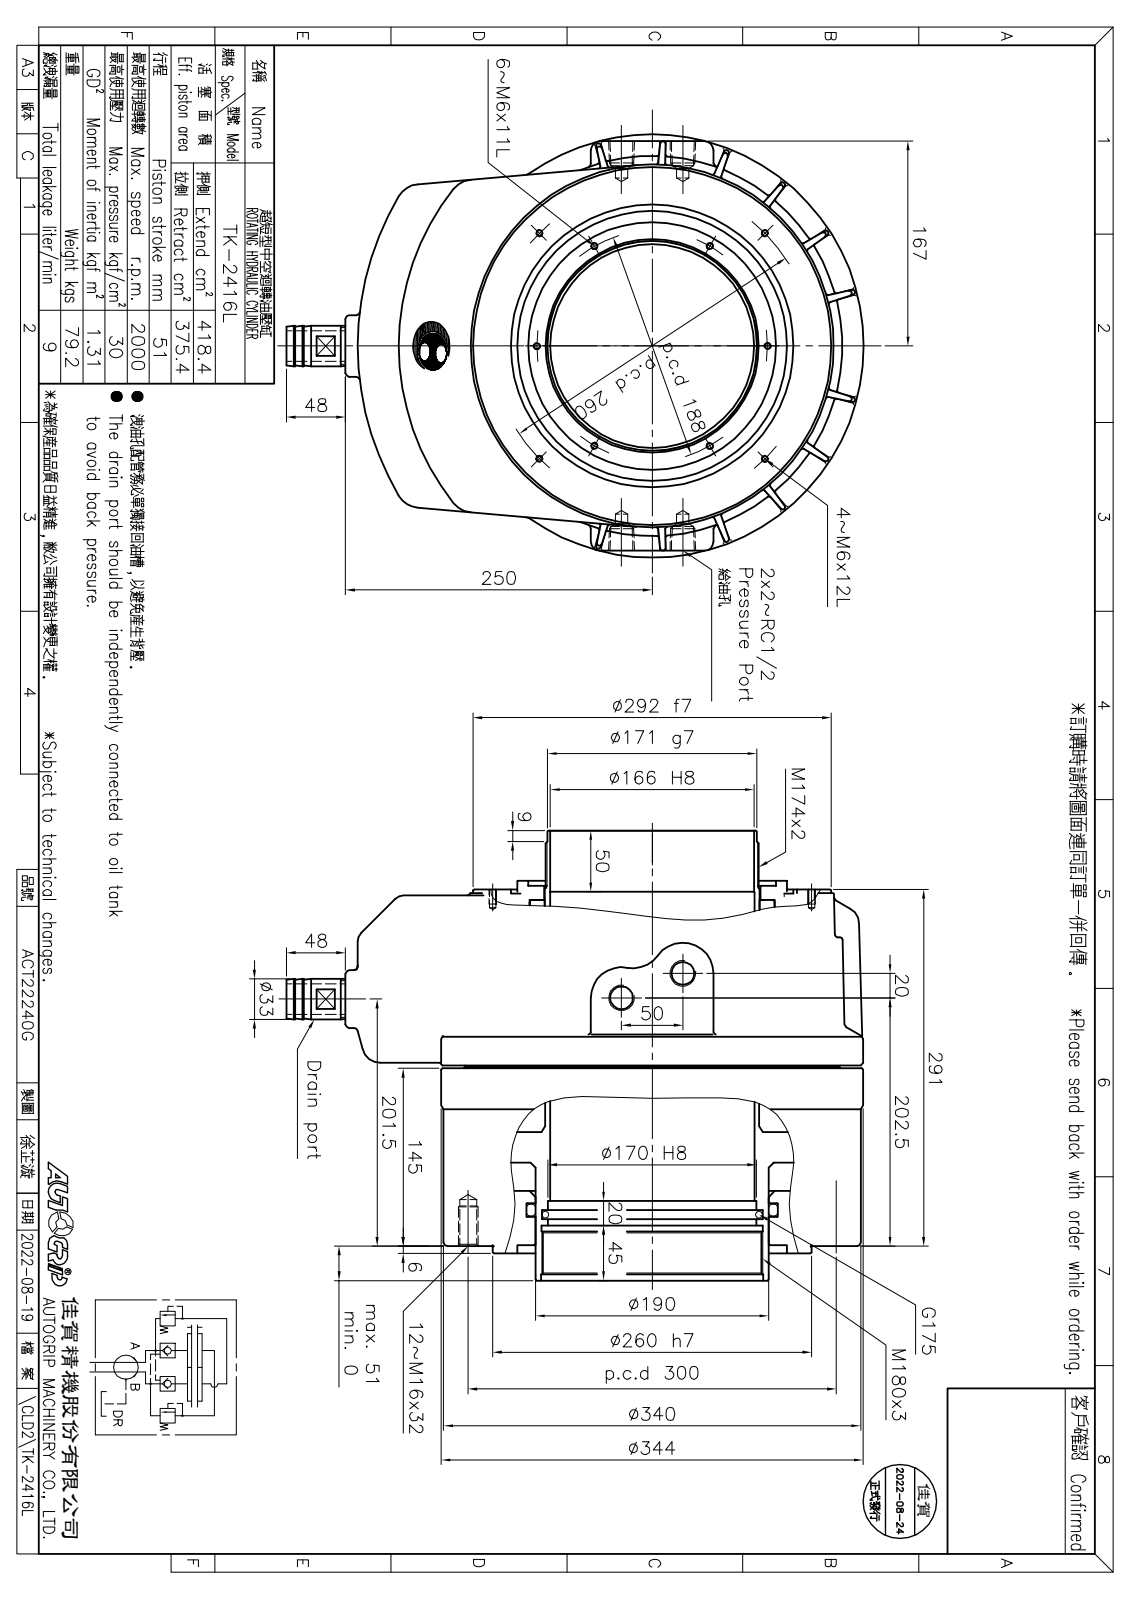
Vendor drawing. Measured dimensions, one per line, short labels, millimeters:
name: CF-TK-2416L; O-RING_G175(NOK); CF-TK-2416後柵環; CF-TK-2416L-02000 (+2 more)
written by: SolidWorks 2020 (CONFIG_CONTROL_DESIGN)
unit: mm
bodies: 7 solids, 805 faces (132 planar, 274 cylindrical, 399 other)
size: 470.5 × 367 × 345
volume: 21 620 000 mm³; area: 1 641 000 mm²
holes: 16× ⌀5, 12× ⌀14, 6× ⌀4.1, 2× ⌀10, 2× ⌀18.5, 1× ⌀25, 1× ⌀30, 1× ⌀166, 1× ⌀166.6, 1× ⌀170, 1× ⌀175, 1× ⌀176
bosses: 1× ⌀345, 1× ⌀340, 1× ⌀292, 1× ⌀260, 1× ⌀234, 1× ⌀215, 1× ⌀210, 1× ⌀174
rounds: 48× R2, 20× R1.5, 12× R15, 4× R7.5, 4× R10, 3× R25, 2× R20, 1× R240
face distances: 36, 1, 146.5, 35, 147.5, 111.5, 144.5, 2.5, 3, 141
hole spacings: 150, 94, 259.81, 289.78, 75, 198.49, 212.13, 162.81
